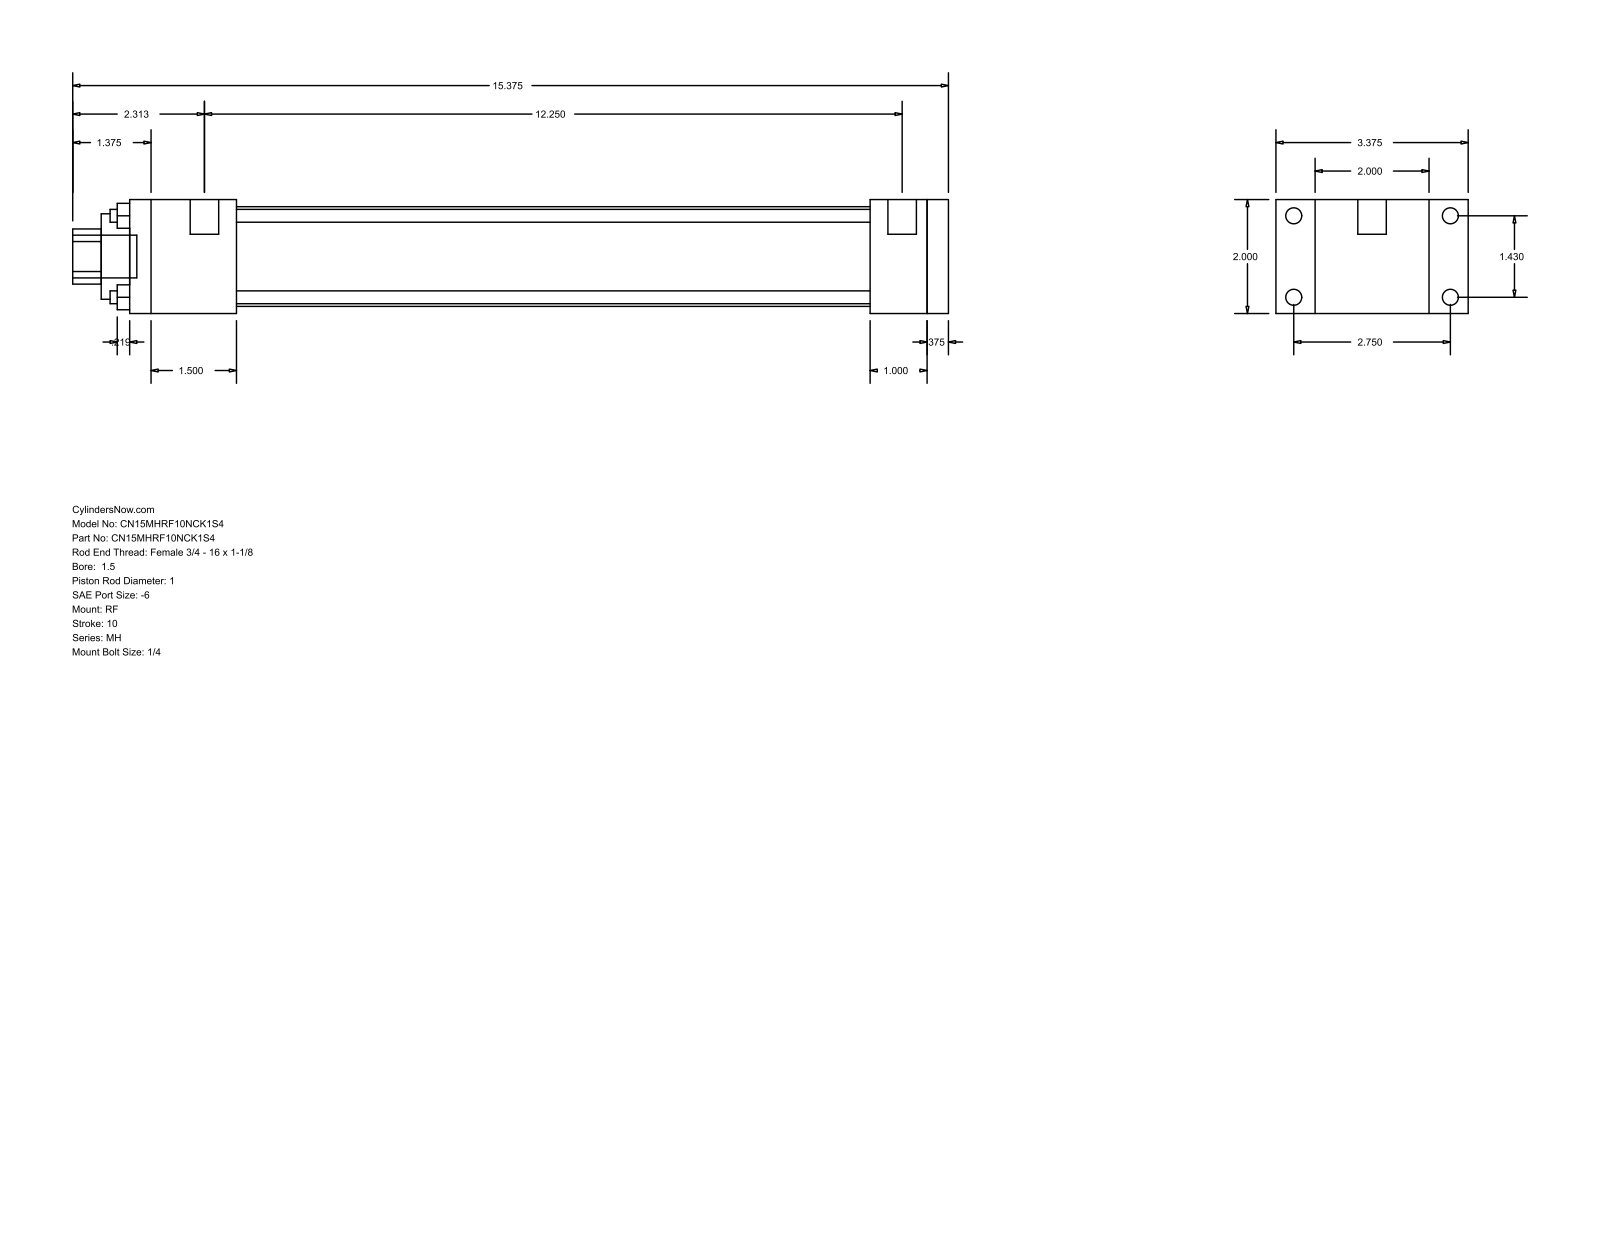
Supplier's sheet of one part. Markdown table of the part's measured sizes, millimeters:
| quantity | value |
| --- | --- |
| part name | MH_RF__0150_1 |
| STEP written by | GSSL Pune (CONFIG_CONTROL_DESIGN) |
| units | millimeters |
| bodies | 0 solids, 92 faces (64 planar, 28 cylindrical, 0 other) |
| overall size | 390.52 × 85.72 × 50.8 |
| round holes (diameter × count) | 5.71 × 4, 25.4 × 1, 38.1 × 1, 44.45 × 1 |
| round bosses / shafts (diameter × count) | 7.14 × 4, 5.56 × 4, 12.7 × 2, 19.05 × 1 |
| partial cylindrical surfaces (radius × count) | 12.29 × 1 |
| main face-to-face distances | 50.8, 9.52, 355.6, 25.4, 365.12, 17.46, 68.26, 330.2, 34.92, 47.63 |
| hole center spacings | 25.68, 36.32, 51.36 |
